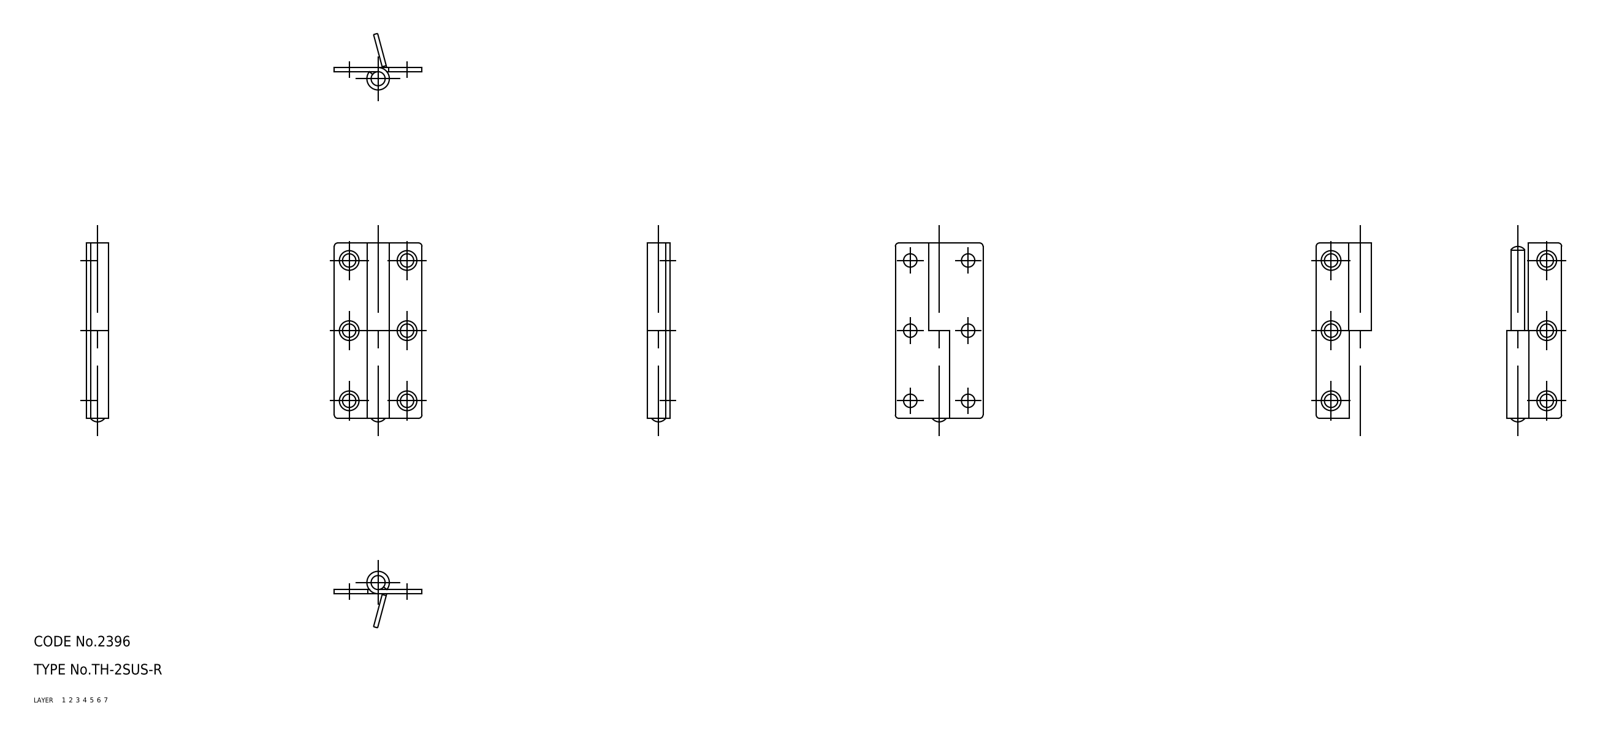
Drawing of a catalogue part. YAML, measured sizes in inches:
part_name: "shaft; hinge piece_B; hinge piece_A; TH_2SUS_R_7520_36"
step_written_by: "CADfix (AUTOMOTIVE_DESIGN)"
units: inches
bodies: {solids: 3, faces: 52, planar: 0, cylindrical: 0, other: 52}
overall_size: [2.008, 0.984, 0.252]
volume: 0.162
surface_area: 6.994
